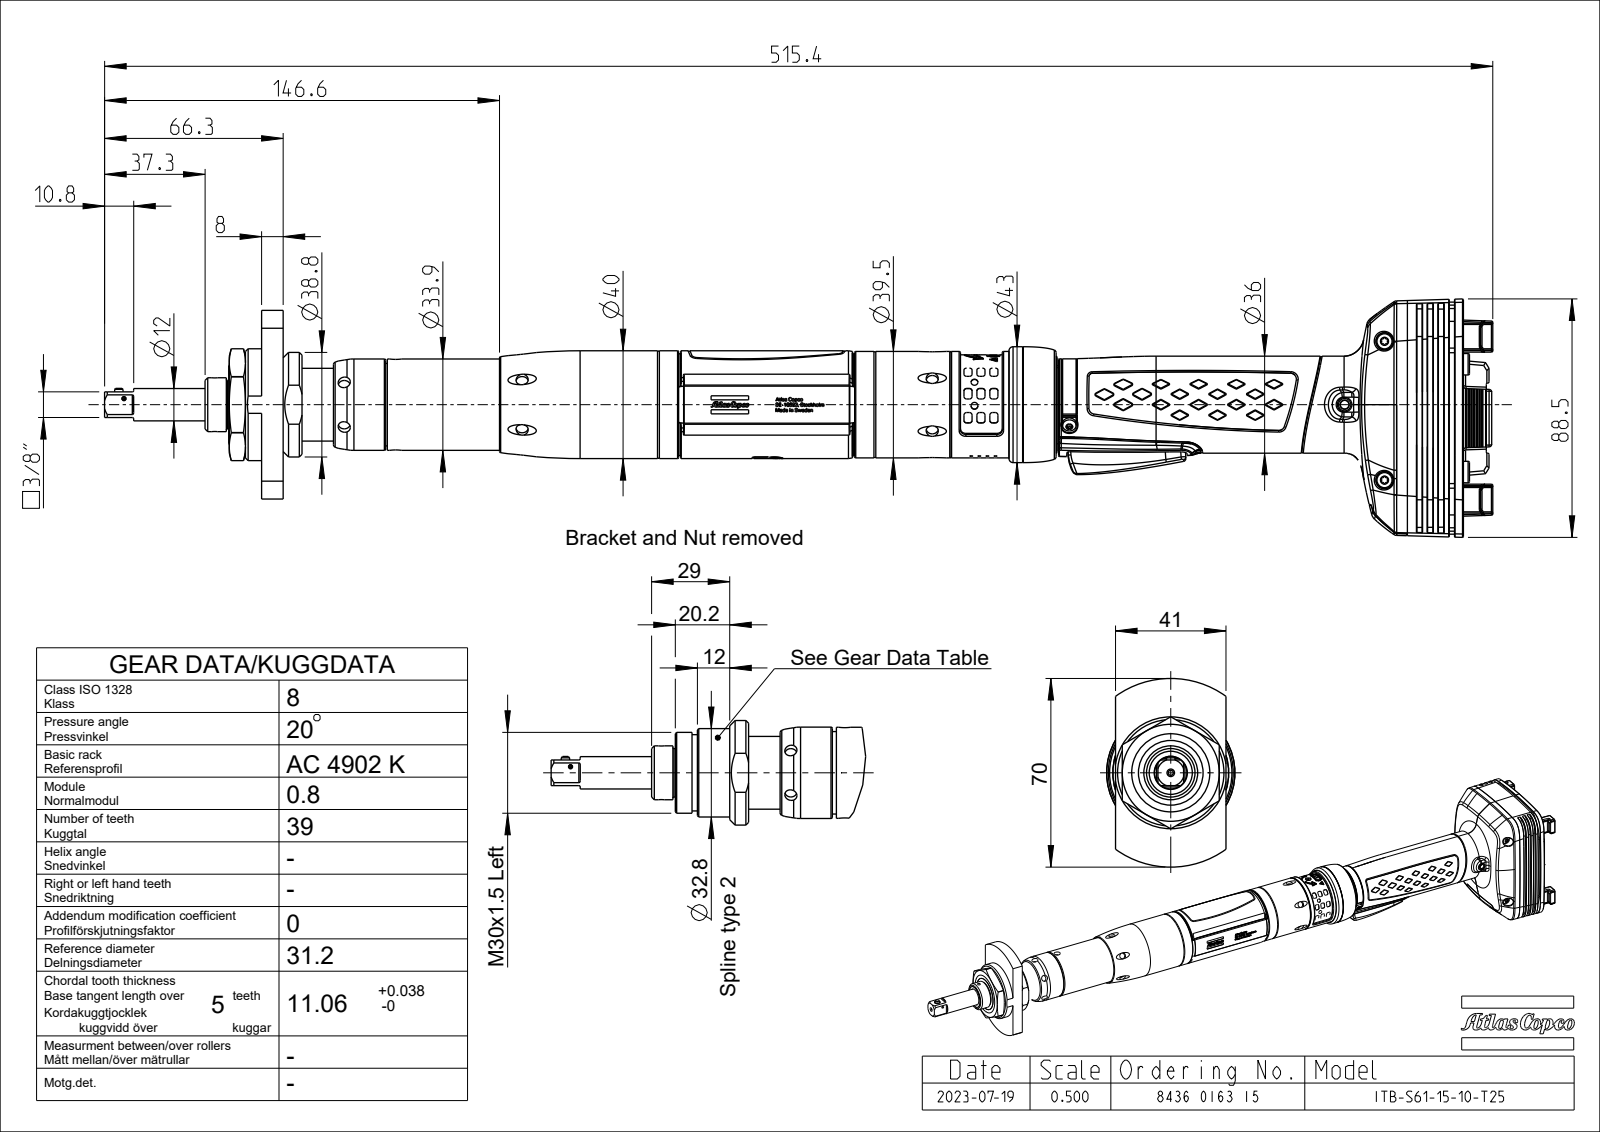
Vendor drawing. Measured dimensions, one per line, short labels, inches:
name: EXT_COMP_SW0008
written by: CREO PARAMETRIC BY PTC INC, 2020281 (CONFIG_CONTROL_DESIGN)
unit: in
bodies: 1 solid, 4763 faces (1439 planar, 988 cylindrical, 2336 other)
size: 20.289 × 3.484 × 2.935
volume: 41.25 in³; area: 152.4 in²
holes: 12× ⌀0.039, 10× ⌀0.177, 2× ⌀0.063, 2× ⌀0.197, 1× ⌀0.059, 1× ⌀0.075, 1× ⌀0.087, 1× ⌀0.126, 1× ⌀0.138, 1× ⌀0.154, 1× ⌀0.186, 1× ⌀0.472
bosses: 2× ⌀0.22, 1× ⌀1.693, 1× ⌀1.575, 1× ⌀1.555, 1× ⌀1.417, 1× ⌀1.335, 1× ⌀1.291, 1× ⌀1.205
rounds: 106× R0.02, 56× R0.039, 37× R0.012, 28× R0.008, 26× R0.079, 18× R0.009, 18× R0.016, 12× R0.011
face distances: 0.199, 0.079, 0.157, 0.236, 0.315, 0.413, 0.039, 0.016, 1.329, 0.394
hole spacings: 0.118, 0.236, 0.354, 2.6, 6.014, 8.614, 0.175, 0.197
